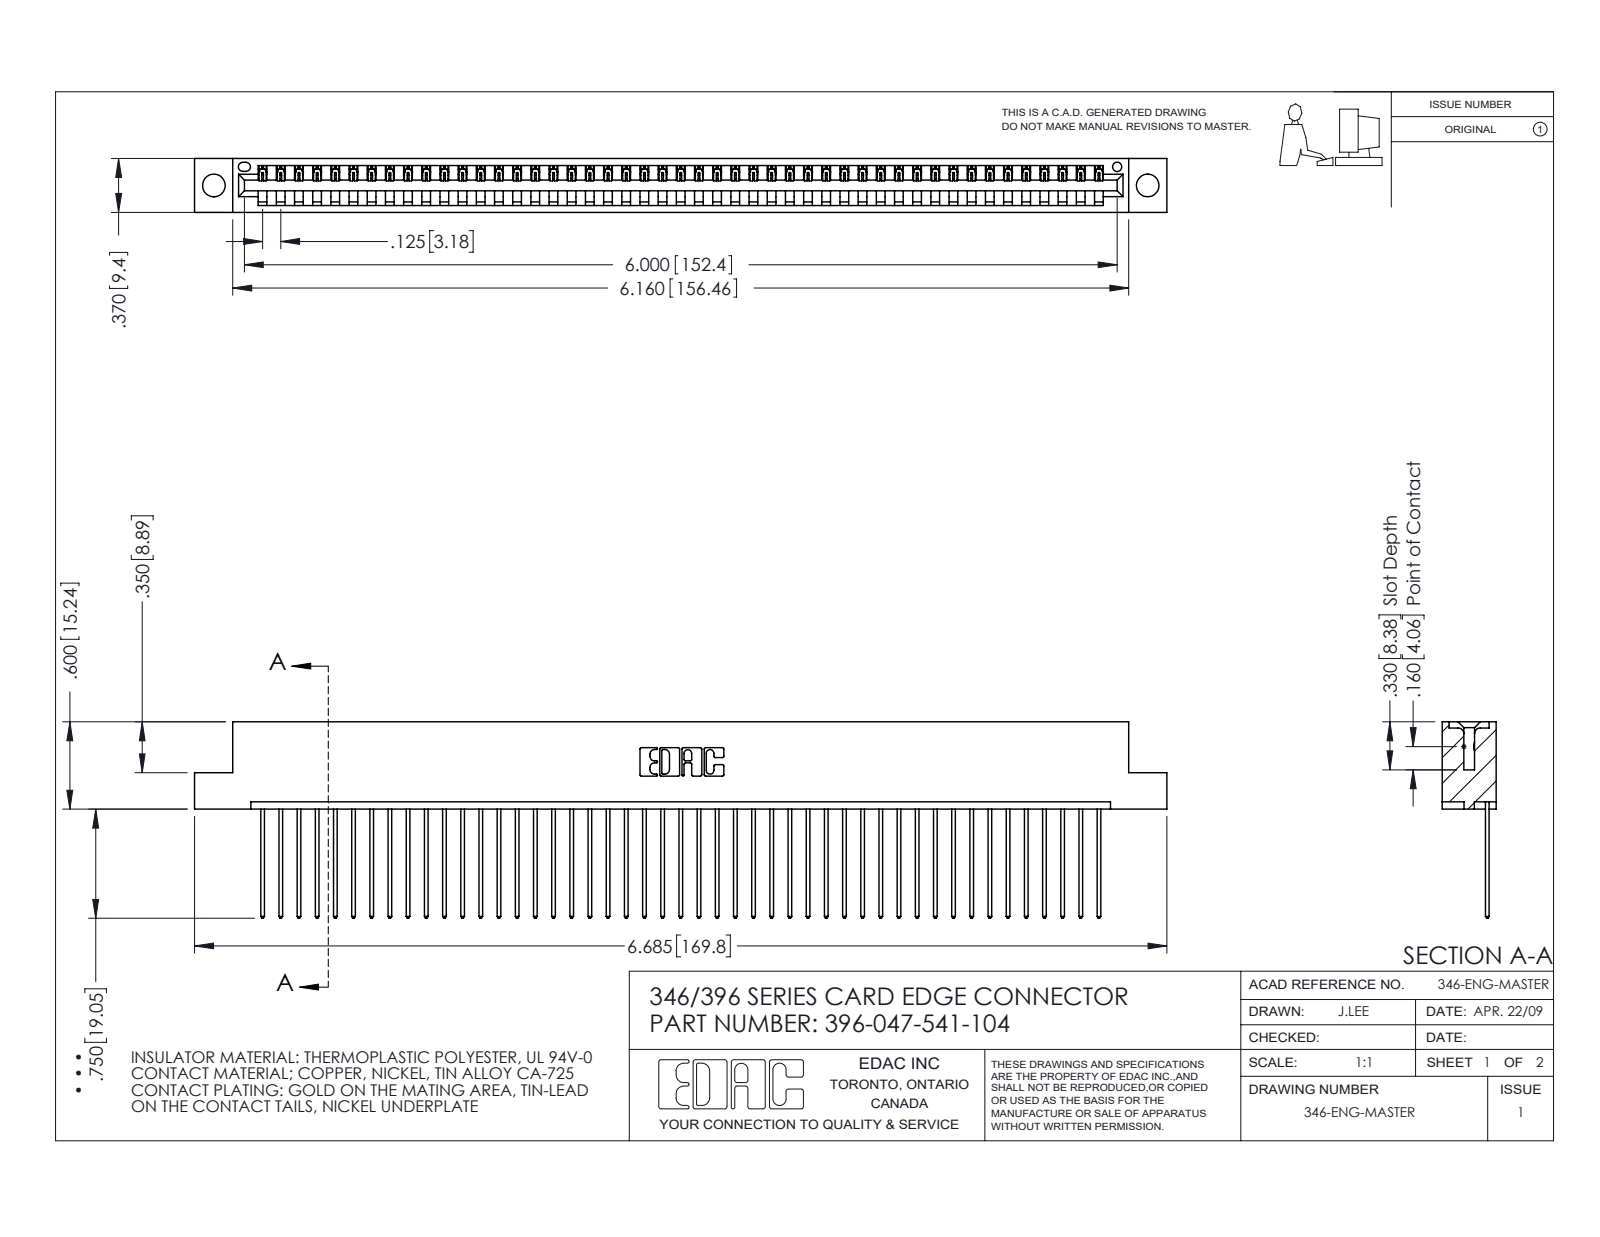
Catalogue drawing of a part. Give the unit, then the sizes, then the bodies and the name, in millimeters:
Units: millimetres
Overall size (bounding box): 169.8 × 34.3 × 9.4
Round holes (diameter × count): ⌀4 ×2, ⌀1.6 ×1
Partial cylindrical surfaces — rounded edges, fillets, slot ends (radius × count): R0.2 ×94, R0.3 ×94, R0.3 ×22, R0.2 ×6, R0.8 ×6, R0.7 ×3, R0.8 ×2, R1 ×2
Main face-to-face distances: 1.2, 8.2, 9.4, 6.4, 1.8, 7.6, 0.6, 3.8, 5.6, 2.5
Hole centre spacings: 6.2, 157.8, 163.1
Volume: 16 400 mm³ · Surface area: 21 230 mm²
Bodies: 48 solids, 2848 faces (1956 planar, 892 cylindrical, 0 other)
Part name (STEP PRODUCT): 345-292-001_345-293-141; 396-047-541-104; 346 Part_Flush Mounting Lugs - 0.156 Dia-TH
STEP written by: SolidWorks 2016 (CONFIG_CONTROL_DESIGN)
